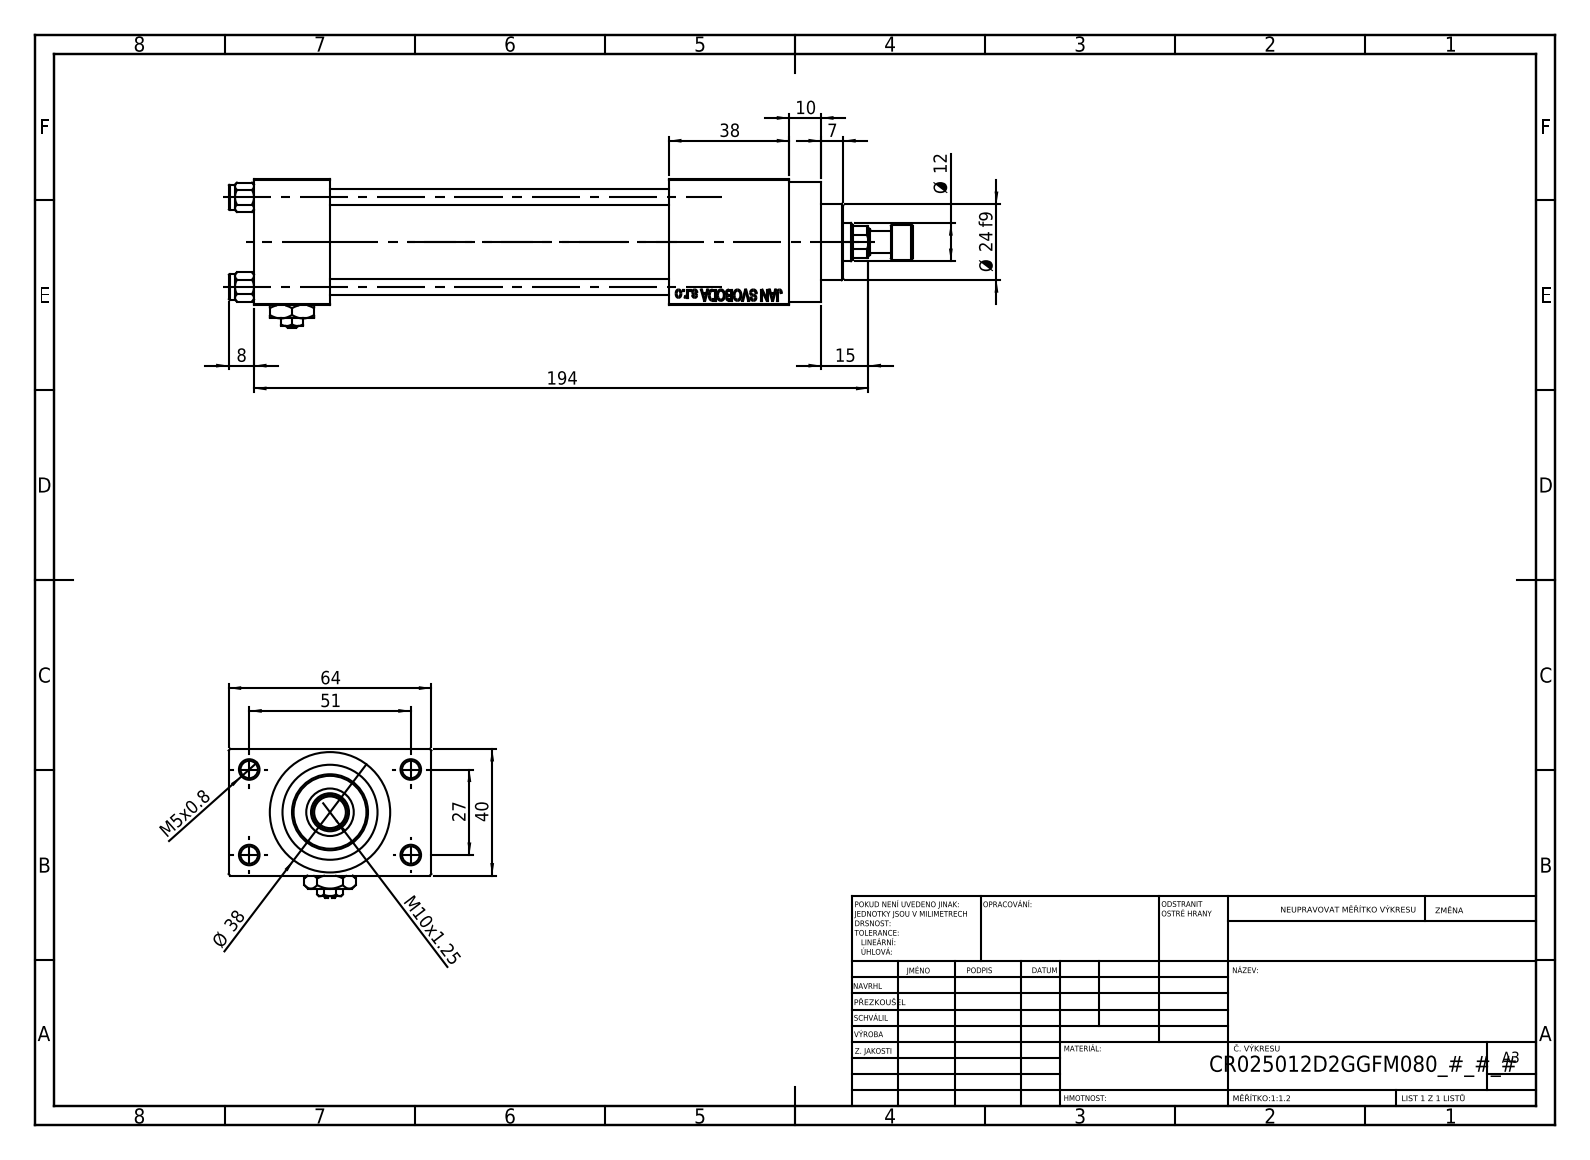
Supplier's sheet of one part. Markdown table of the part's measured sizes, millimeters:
| quantity | value |
| --- | --- |
| part name | V215CR_D_Body; V215CR_ROD_END_F; V215CR_D_TYCINKA; NUT_M5_D (+3 more) |
| STEP written by | SolidWorks 2019 (CONFIG_CONTROL_DESIGN) |
| units | millimeters |
| bodies | 13 solids, 1169 faces (523 planar, 100 cylindrical, 546 other) |
| overall size | 216 × 64 × 47 |
| volume | 202 432 mm³ |
| surface area | 79 956 mm² |
| round holes (diameter × count) | 5 × 4, 5.5 × 4, 20 × 3, 7 × 2, 13.16 × 2, 6.5 × 1, 12 × 1, 15 × 1, 25 × 1, 30 × 1 |
| round bosses / shafts (diameter × count) | 8 × 4, 38 × 1, 31 × 1, 24 × 1, 11 × 1 |
| main face-to-face distances | 40, 12, 52, 107, 24, 131, 64, 38, 169, 145 |
| hole center spacings | 11.37, 20.01, 28.3, 28.85, 29.89, 39.66, 48.34, 27 |
